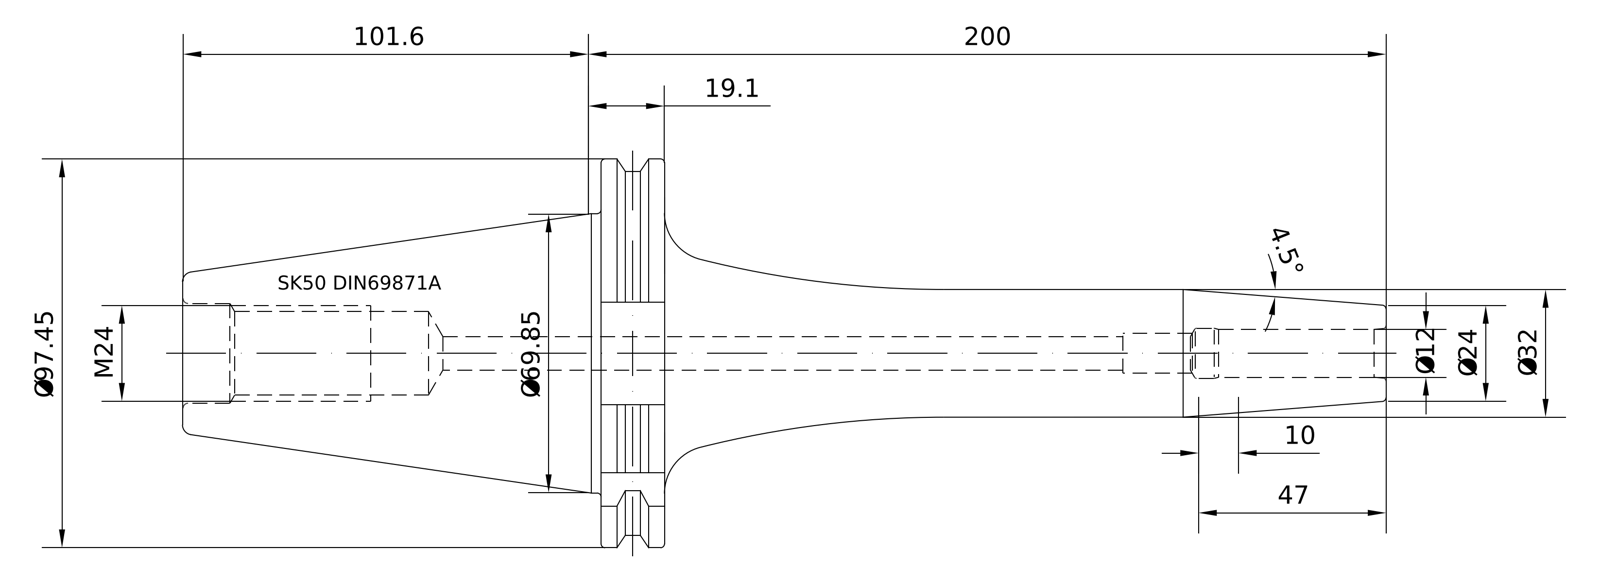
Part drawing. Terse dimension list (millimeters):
name: 50-446-12
written by: PRO/ENGINEER BY PARAMETRIC TECHNOLOGY CORPORATION, 2010430 (CONFIG_CONTROL_DESIGN)
unit: mm
bodies: 1 solid, 95 faces (21 planar, 24 cylindrical, 50 other)
size: 301.6 × 97.47 × 94
volume: 500 600 mm³; area: 61 471 mm²
holes: 1× ⌀12, 1× ⌀20.75, 1× ⌀25.01, 1× ⌀25.7
bosses: 1× ⌀91, 1× ⌀69.15, 1× ⌀32, 1× ⌀24.01
rounds: 1× R1.75, 1× R48.74
face distances: 15.85, 72.8, 104.8, 120.65, 25.8, 301.6, 196.8, 180.95, 48, 56.8
